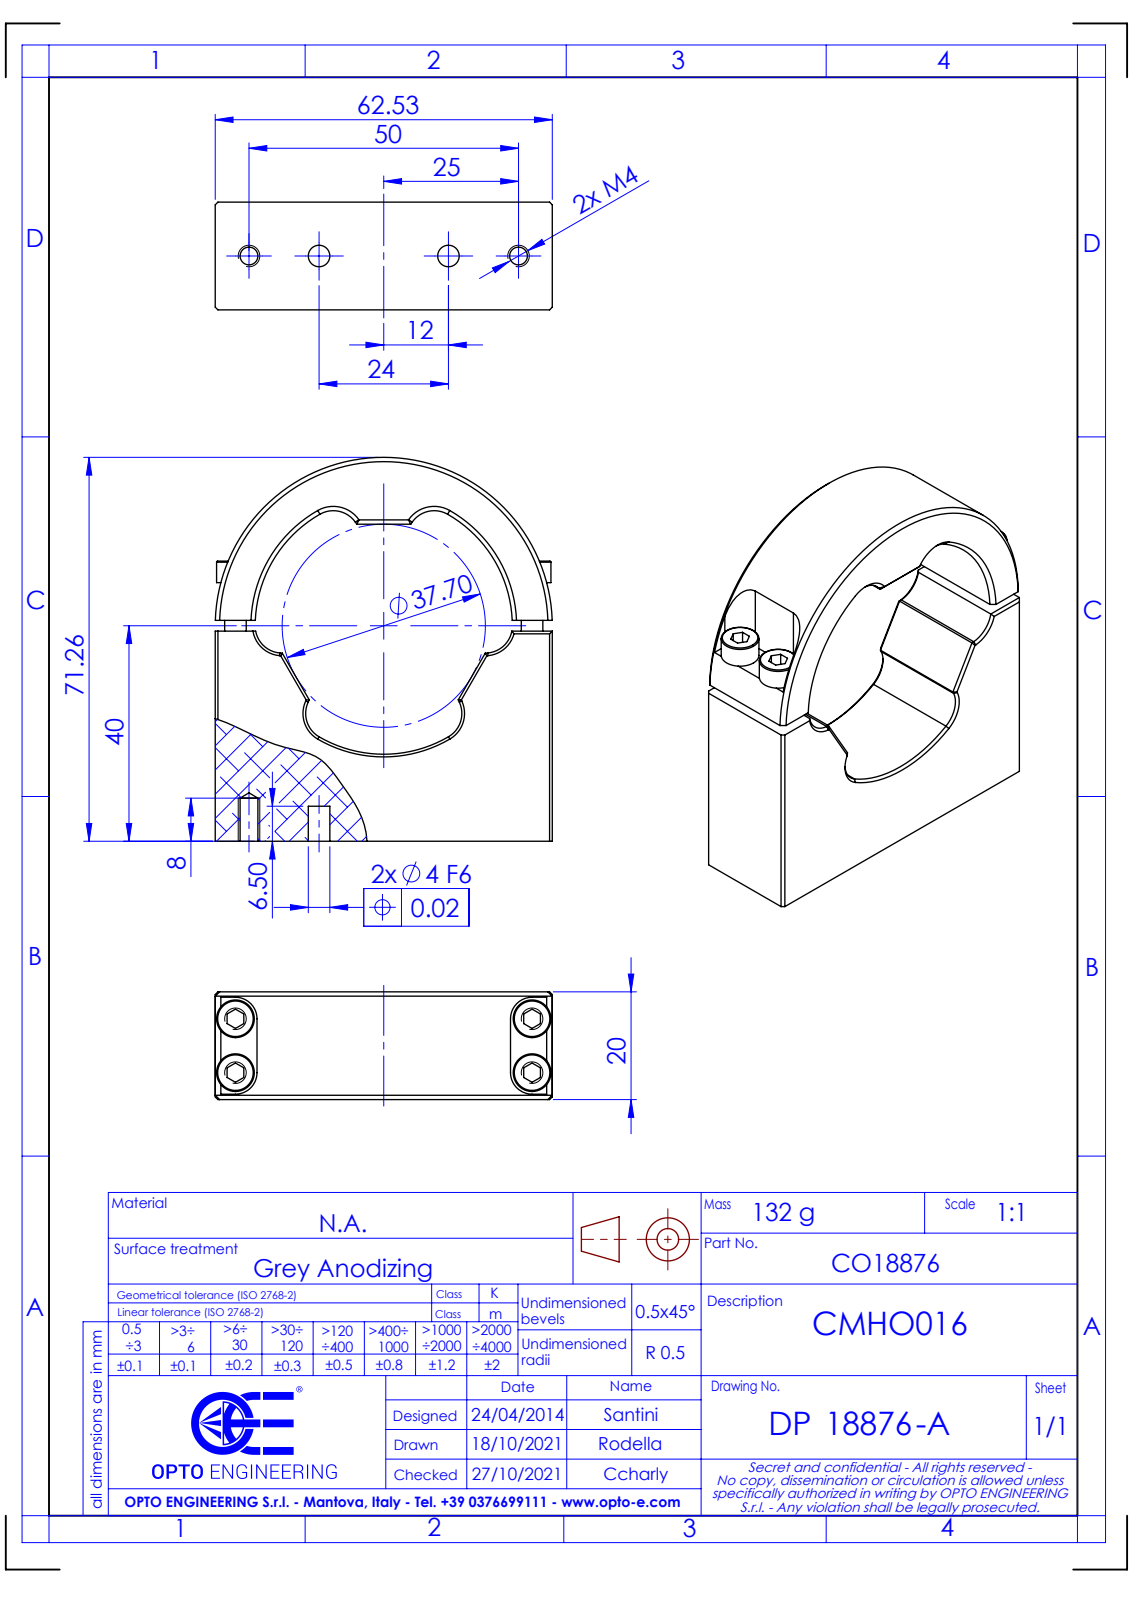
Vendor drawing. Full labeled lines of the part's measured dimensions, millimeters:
Part name (STEP PRODUCT): DP18876-A_CMHO016
STEP written by: SolidWorks 2021 (CONFIG_CONTROL_DESIGN)
Units: millimetres
Bodies: 0 solids, 156 faces (79 planar, 47 cylindrical, 30 other)
Overall size (bounding box): 71.26 × 62.53 × 20
Round holes (diameter × count): ⌀4.5 ×4, ⌀3.3 ×2, ⌀4 ×2
Round bosses / shafts (diameter × count): ⌀7 ×4, ⌀4 ×4
Partial cylindrical surfaces — rounded edges, fillets, slot ends (radius × count): R5 ×6, R4 ×4, R23.85 ×1, R31.26 ×1
Main face-to-face distances: 20, 62.52, 39, 48, 9, 7.75, 54.77, 41, 2, 7
Hole centre spacings: 5.59, 16.3, 39.83, 52.75, 10, 13, 37, 55.02
